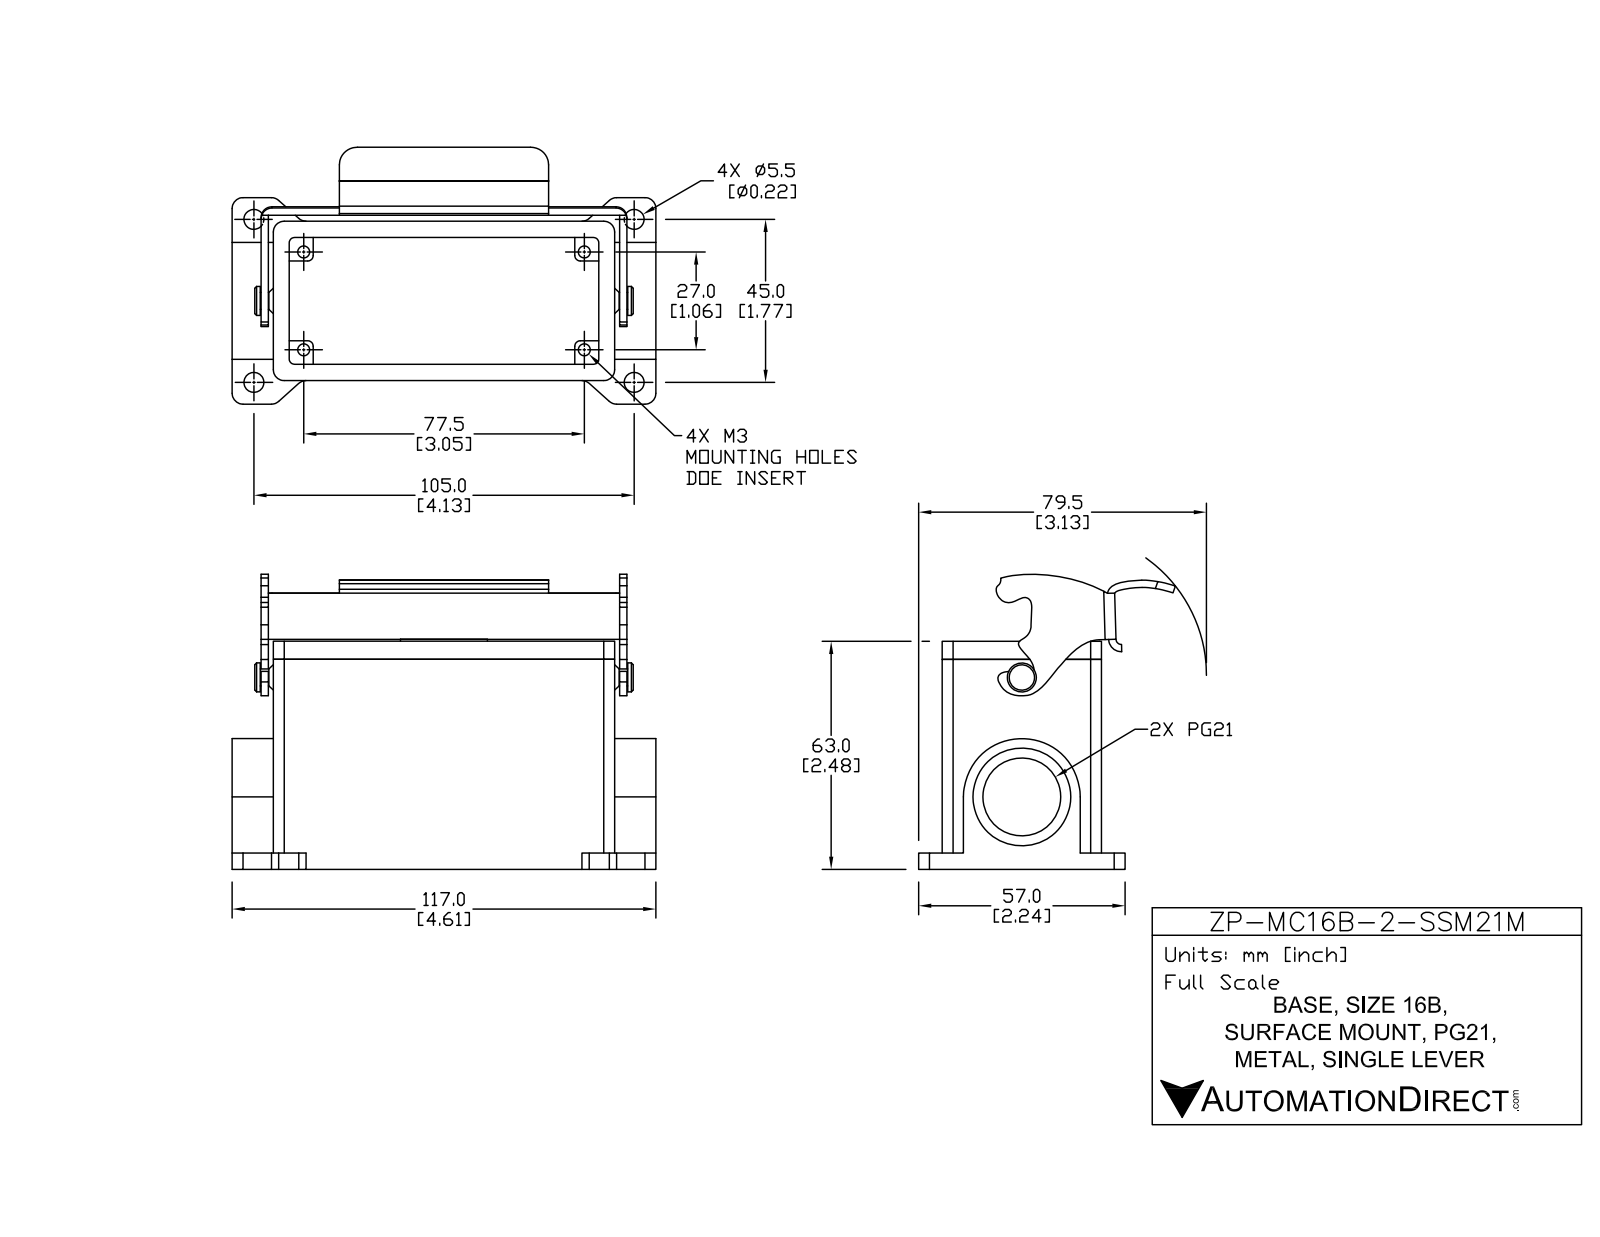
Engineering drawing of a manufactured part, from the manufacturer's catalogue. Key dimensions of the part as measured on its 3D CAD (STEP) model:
Part name (STEP PRODUCT): ZP-MC16B-2-SSM21M
STEP written by: SolidWorks 2011 (AUTOMOTIVE_DESIGN)
Units: millimetres
Bodies: 3 solids, 205 faces (91 planar, 110 cylindrical, 4 other)
Overall size (bounding box): 117 × 77.44 × 76.46
Volume: 98 652 mm³ · Surface area: 55 015 mm²
Round holes (diameter × count): ⌀3.3 ×4, ⌀5.5 ×4, ⌀21.5 ×1, ⌀27 ×1
Round bosses / shafts (diameter × count): ⌀8 ×1, ⌀4.67 ×1
Partial cylindrical surfaces — rounded edges, fillets, slot ends (radius × count): R3 ×17, R0.5 ×13, R1.5 ×8, R2 ×3, R4 ×3, R1 ×2, R10 ×2, R0.92 ×1
Main face-to-face distances: 4.5, 39.5, 44, 35, 2, 1.15, 57, 55, 4.37, 89.87
Hole centre spacings: 16.64, 38.63, 91.44, 97.86, 27, 45, 77, 81.6
